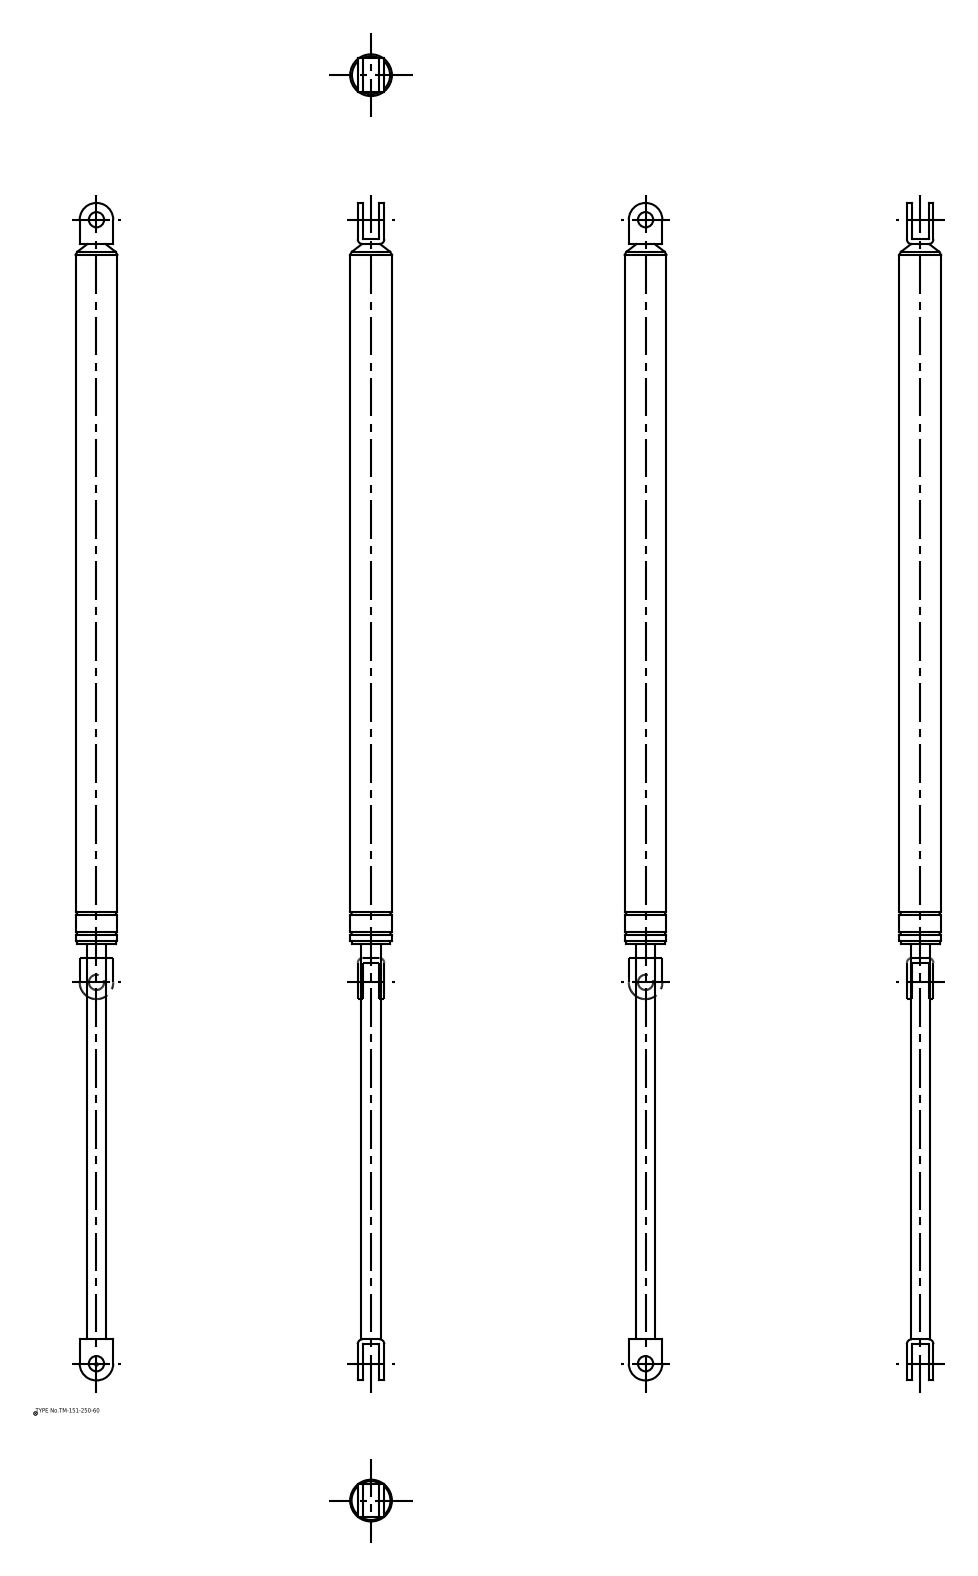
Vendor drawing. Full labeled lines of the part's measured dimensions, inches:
Part name (STEP PRODUCT): TM_151_250_60; TM_151_250_60_div
STEP written by: spGate 16.7.1 (AUTOMOTIVE_DESIGN)
Units: inches
Bodies: 2 solids, 63 faces (21 planar, 30 cylindrical, 12 other)
Overall size (bounding box): 30.394 × 1.079 × 1.079
Volume: 18.78 in³ · Surface area: 87.31 in²
Round holes (diameter × count): ⌀0.394 ×2
Round bosses / shafts (diameter × count): ⌀1.079 ×1, ⌀1.004 ×1, ⌀0.492 ×1
Partial cylindrical surfaces — rounded edges, fillets, slot ends (radius × count): R0.118 ×4, R0.433 ×2
Main face-to-face distances: 0.126, 0.559, 0.685, 0.433, 28.394, 0.866, 10.323, 28.52, 18.197, 18.071
Hole centre spacings: 29.528
